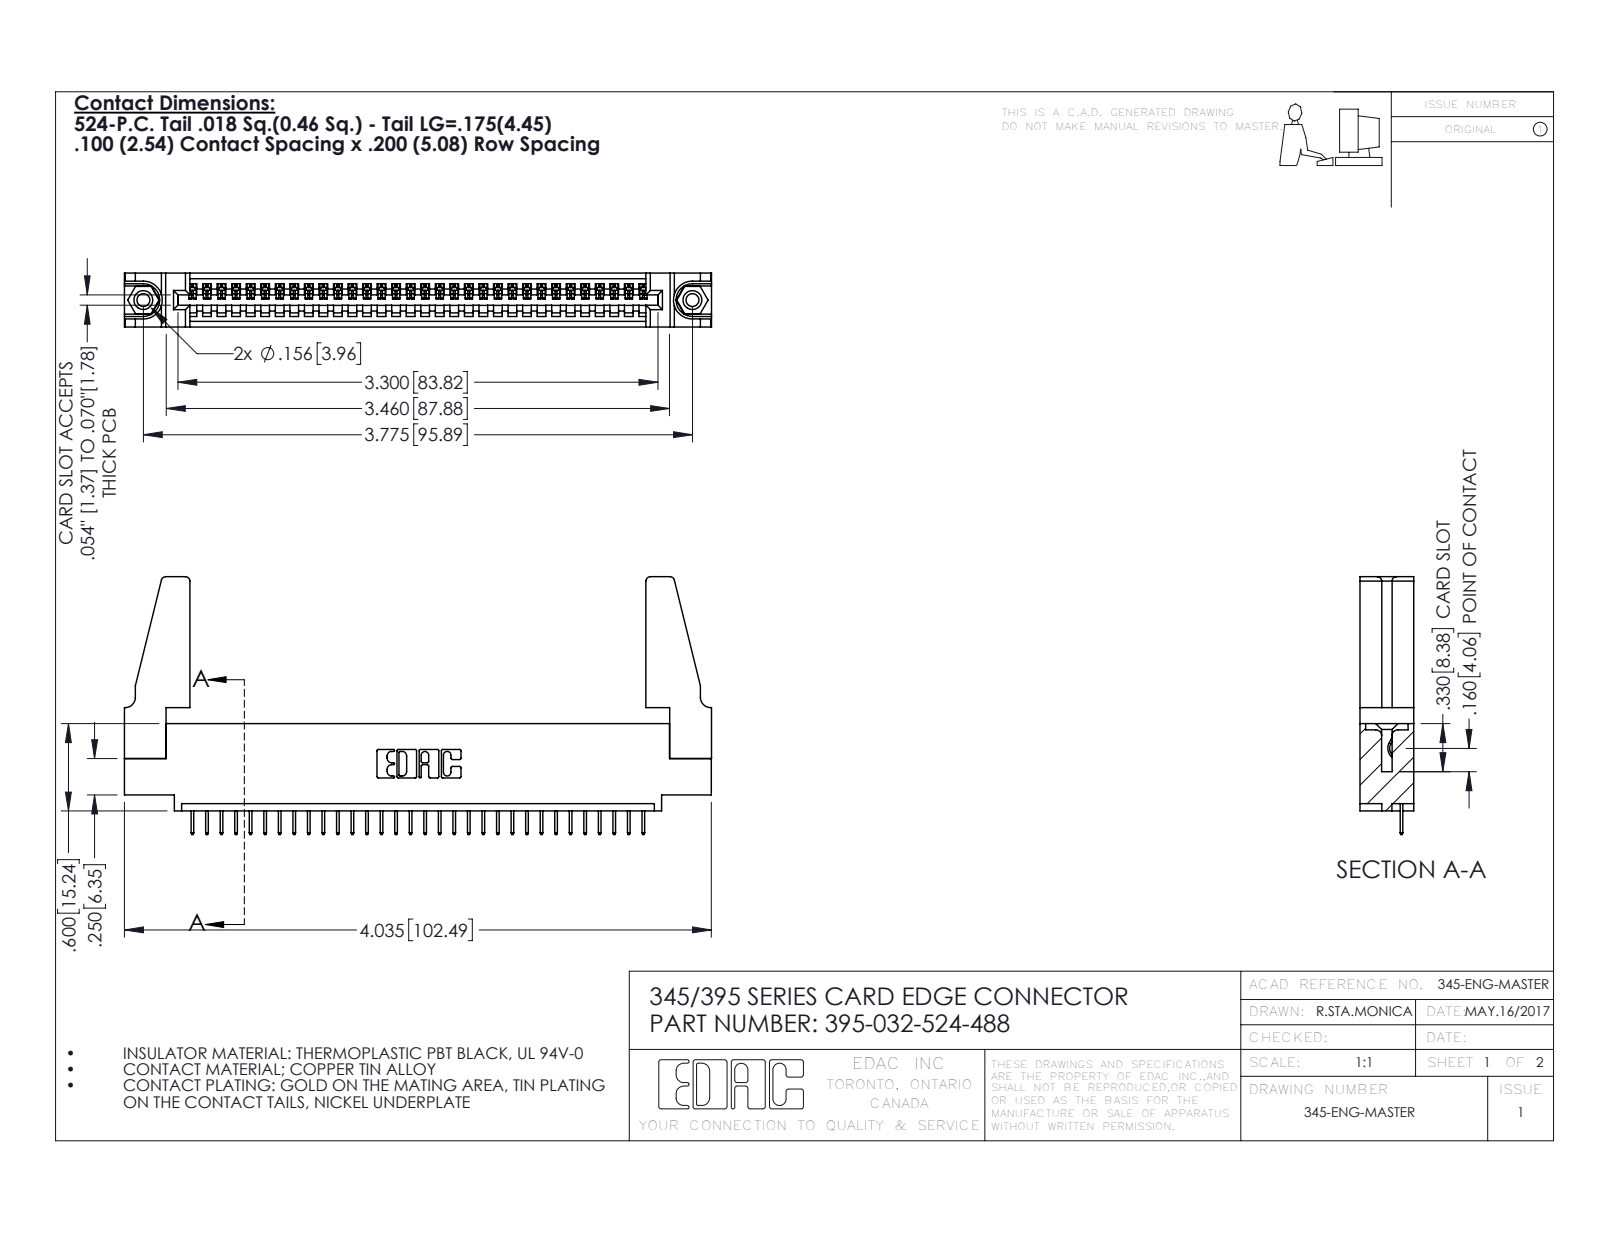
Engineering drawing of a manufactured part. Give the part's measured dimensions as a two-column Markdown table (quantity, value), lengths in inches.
| quantity | value |
| --- | --- |
| part name | 395-032-524-488; 345 Part_0.110 Offset - 0.156 Dia-TH; 345-250-001_345-250-001-102; 345-220-078_345-220-088 (+1 more) |
| STEP written by | SolidWorks 2016 (CONFIG_CONTROL_DESIGN) |
| units | inches |
| bodies | 37 solids, 2238 faces (1628 planar, 594 cylindrical, 16 other) |
| overall size | 4.036 × 1.772 × 0.37 |
| volume | 0.775 in³ |
| surface area | 23.62 in² |
| round holes (diameter × count) | 0.089 × 2, 0.125 × 2, 0.156 × 2, 0.064 × 1 |
| round bosses / shafts (diameter × count) | 0.155 × 2 |
| partial cylindrical surfaces (radius × count) | 0.006 × 64, 0.01 × 22, 0.03 × 8, 0.007 × 6, 0.031 × 6, 0.026 × 3, 0.031 × 2, 0.04 × 2 |
| main face-to-face distances | 0.072, 0.37, 0.298, 0.2, 0.098, 0.272, 0.025, 0.225, 0.072, 0.149 |
| hole center spacings | 0.27, 3.54, 3.775 |
